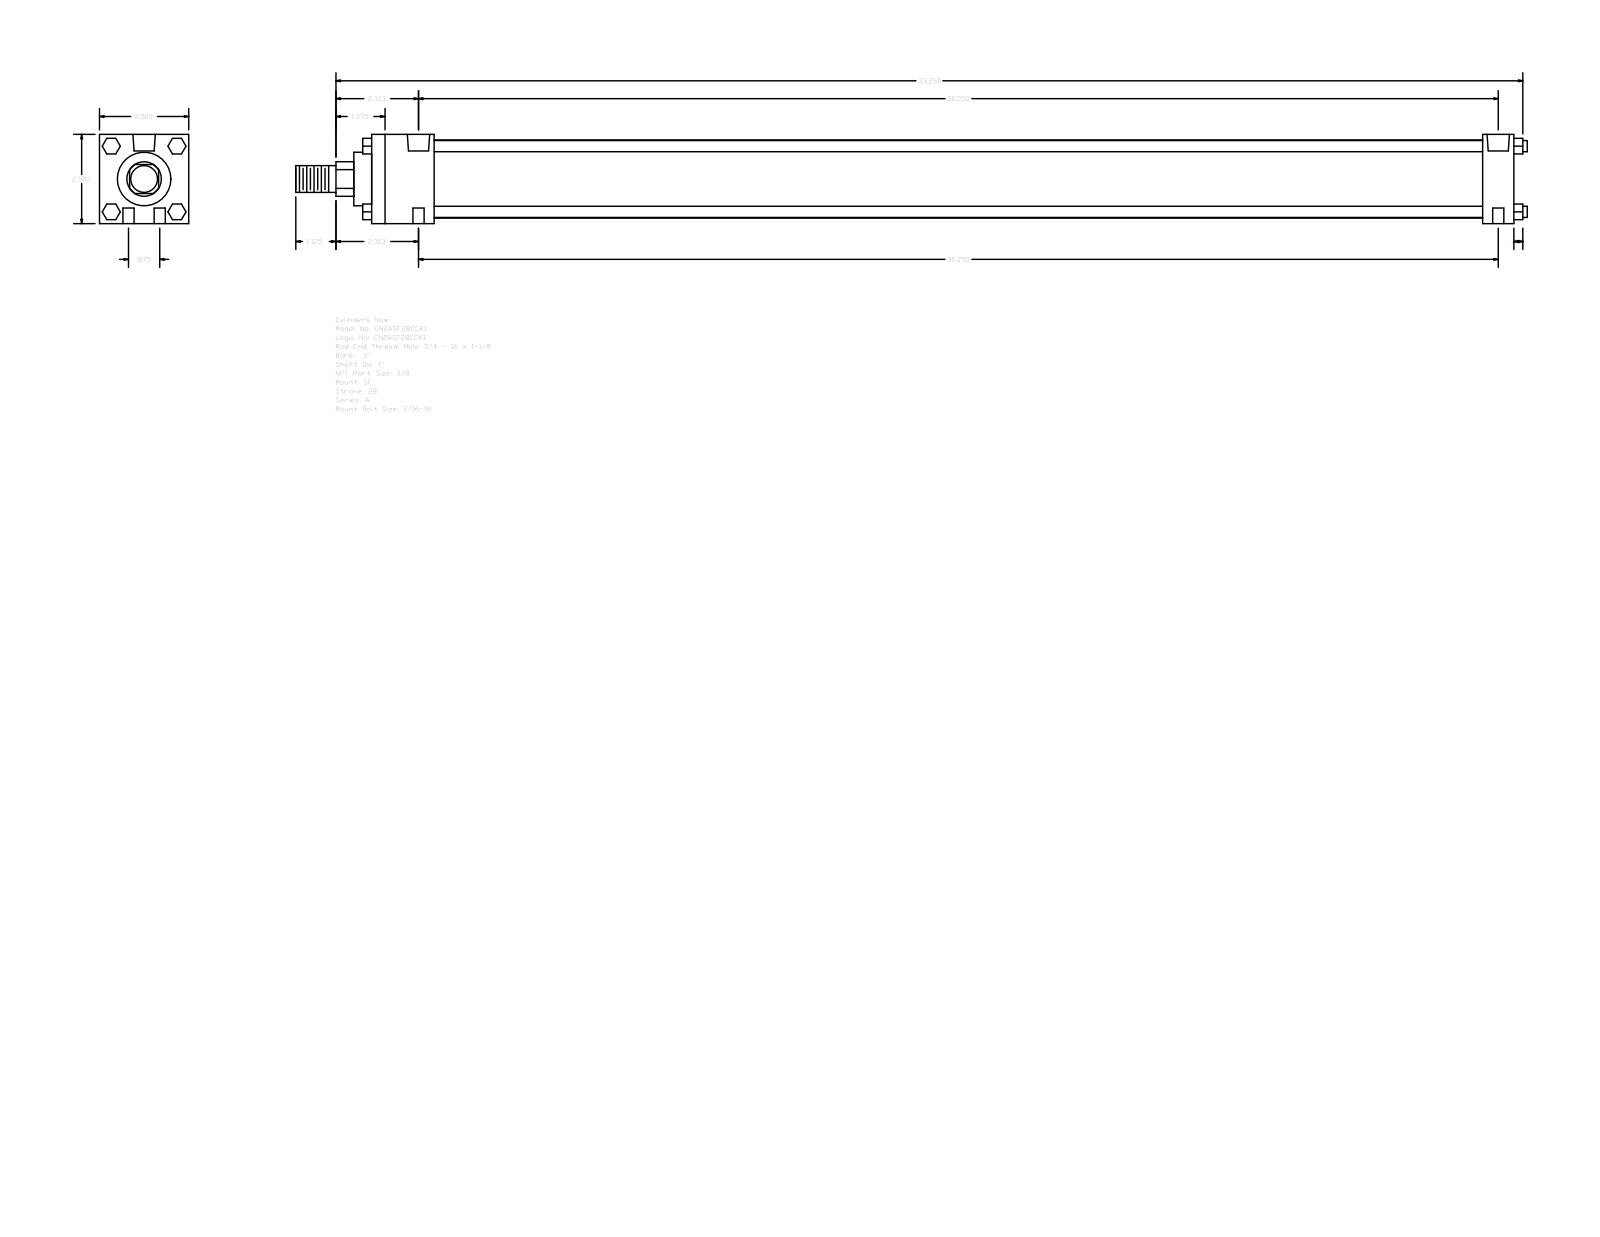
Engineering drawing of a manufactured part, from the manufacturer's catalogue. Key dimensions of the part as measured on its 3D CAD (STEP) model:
Part name (STEP PRODUCT): A_SF__0200_1
STEP written by: GSSL Pune (CONFIG_CONTROL_DESIGN)
Units: millimetres
Bodies: 0 solids, 124 faces (94 planar, 30 cylindrical, 0 other)
Overall size (bounding box): 876.3 × 63.5 × 63.5
Round holes (diameter × count): ⌀7.94 ×4, ⌀5.56 ×2, ⌀15.93 ×2
Round bosses / shafts (diameter × count): ⌀7.94 ×4, ⌀55.63 ×1, ⌀38.1 ×1, ⌀25.4 ×1, ⌀19.05 ×1
Partial cylindrical surfaces — rounded edges, fillets, slot ends (radius × count): R12.29 ×1
Main face-to-face distances: 63.5, 812.8, 790.58, 22.22, 44.45, 746.13, 768.35, 12.7, 825.5, 6.35
Hole centre spacings: 11.11, 768.43, 768.35, 22.22, 768.67, 762.78
